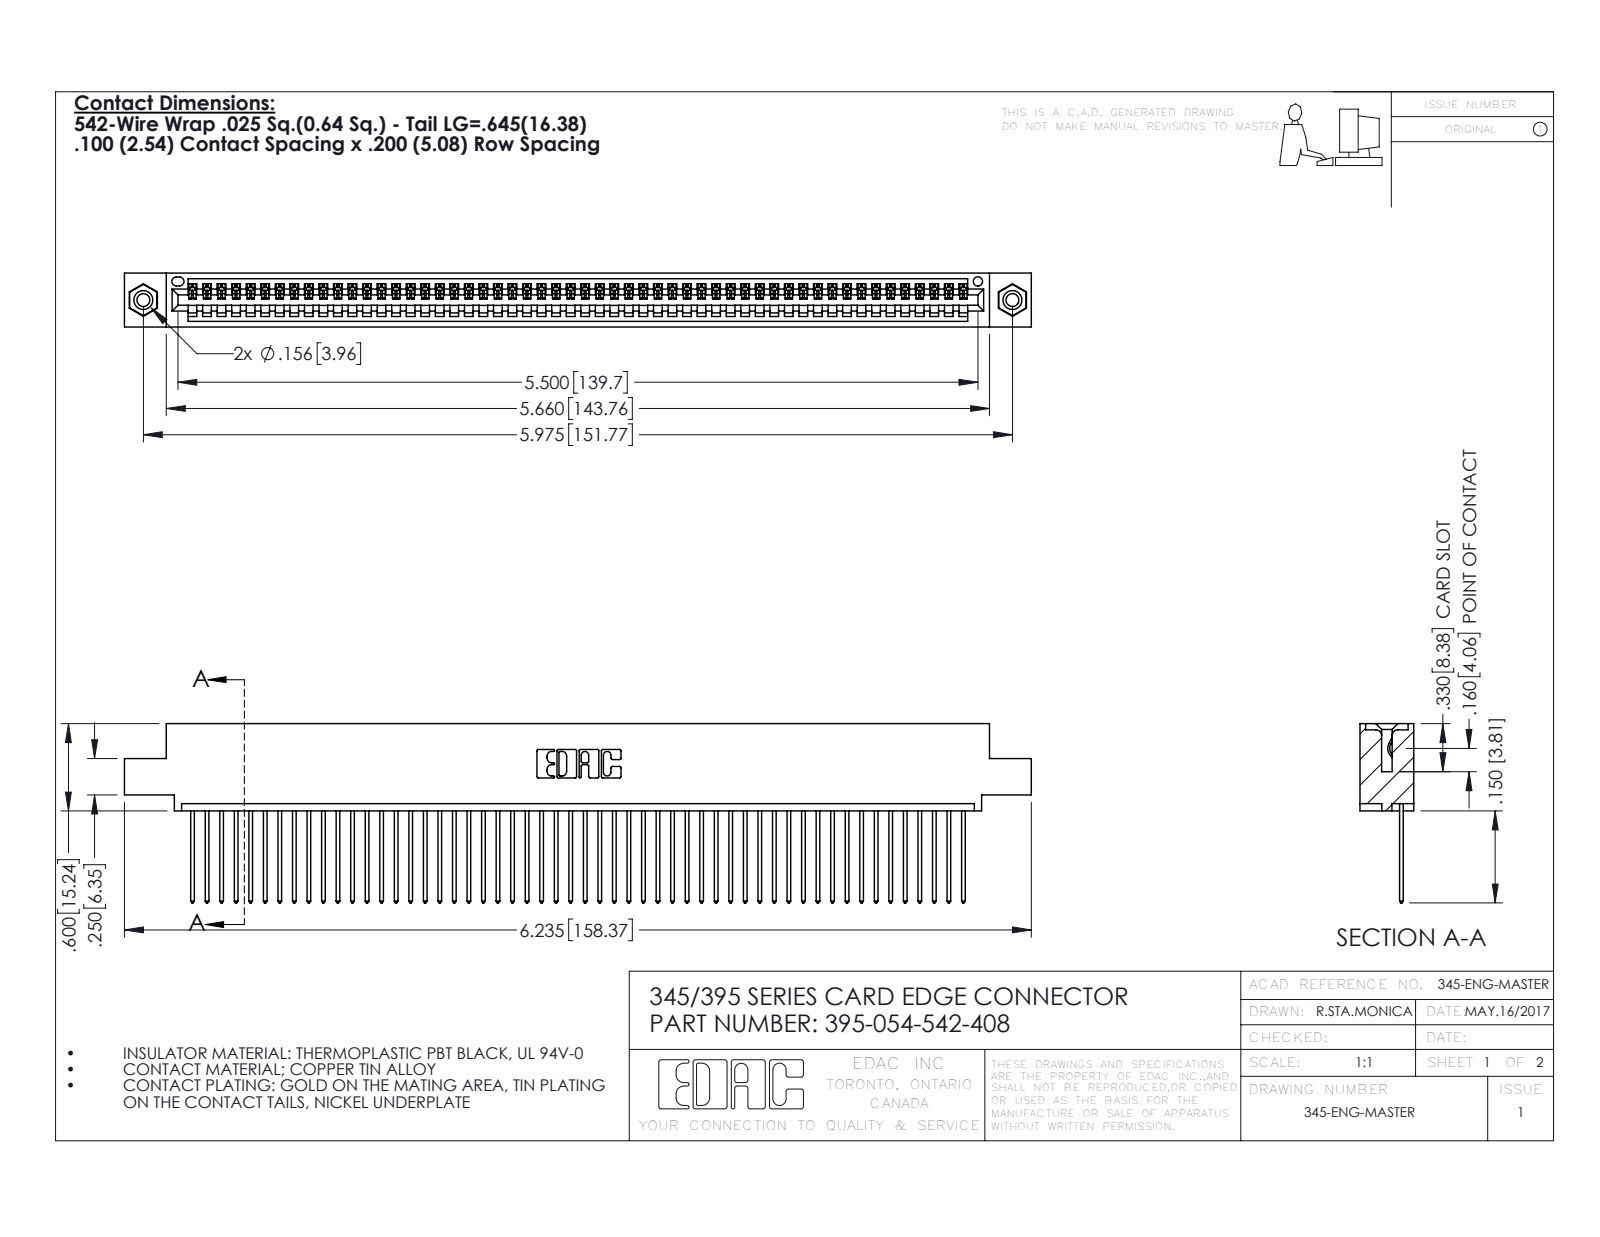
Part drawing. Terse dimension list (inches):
name: 345-292-001_345-293-142; 395-054-542-408; 345 Part_0.110 Offset - 0.156 Dia-TI; 345-250-001_345-250-003-102
written by: SolidWorks 2016 (CONFIG_CONTROL_DESIGN)
unit: in
bodies: 57 solids, 3322 faces (2276 planar, 1030 cylindrical, 16 other)
size: 6.235 × 1.232 × 0.37
volume: 0.926 in³; area: 32.86 in²
holes: 2× ⌀0.089, 2× ⌀0.125, 2× ⌀0.156, 1× ⌀0.064
bosses: 2× ⌀0.155
rounds: 108× R0.006, 108× R0.01, 22× R0.01, 6× R0.007, 6× R0.031, 3× R0.026, 2× R0.031, 2× R0.04
face distances: 0.072, 0.298, 0.098, 0.272, 0.025, 0.37, 0.2, 0.225, 0.149, 0.072
hole spacings: 0.27, 5.739, 5.975
